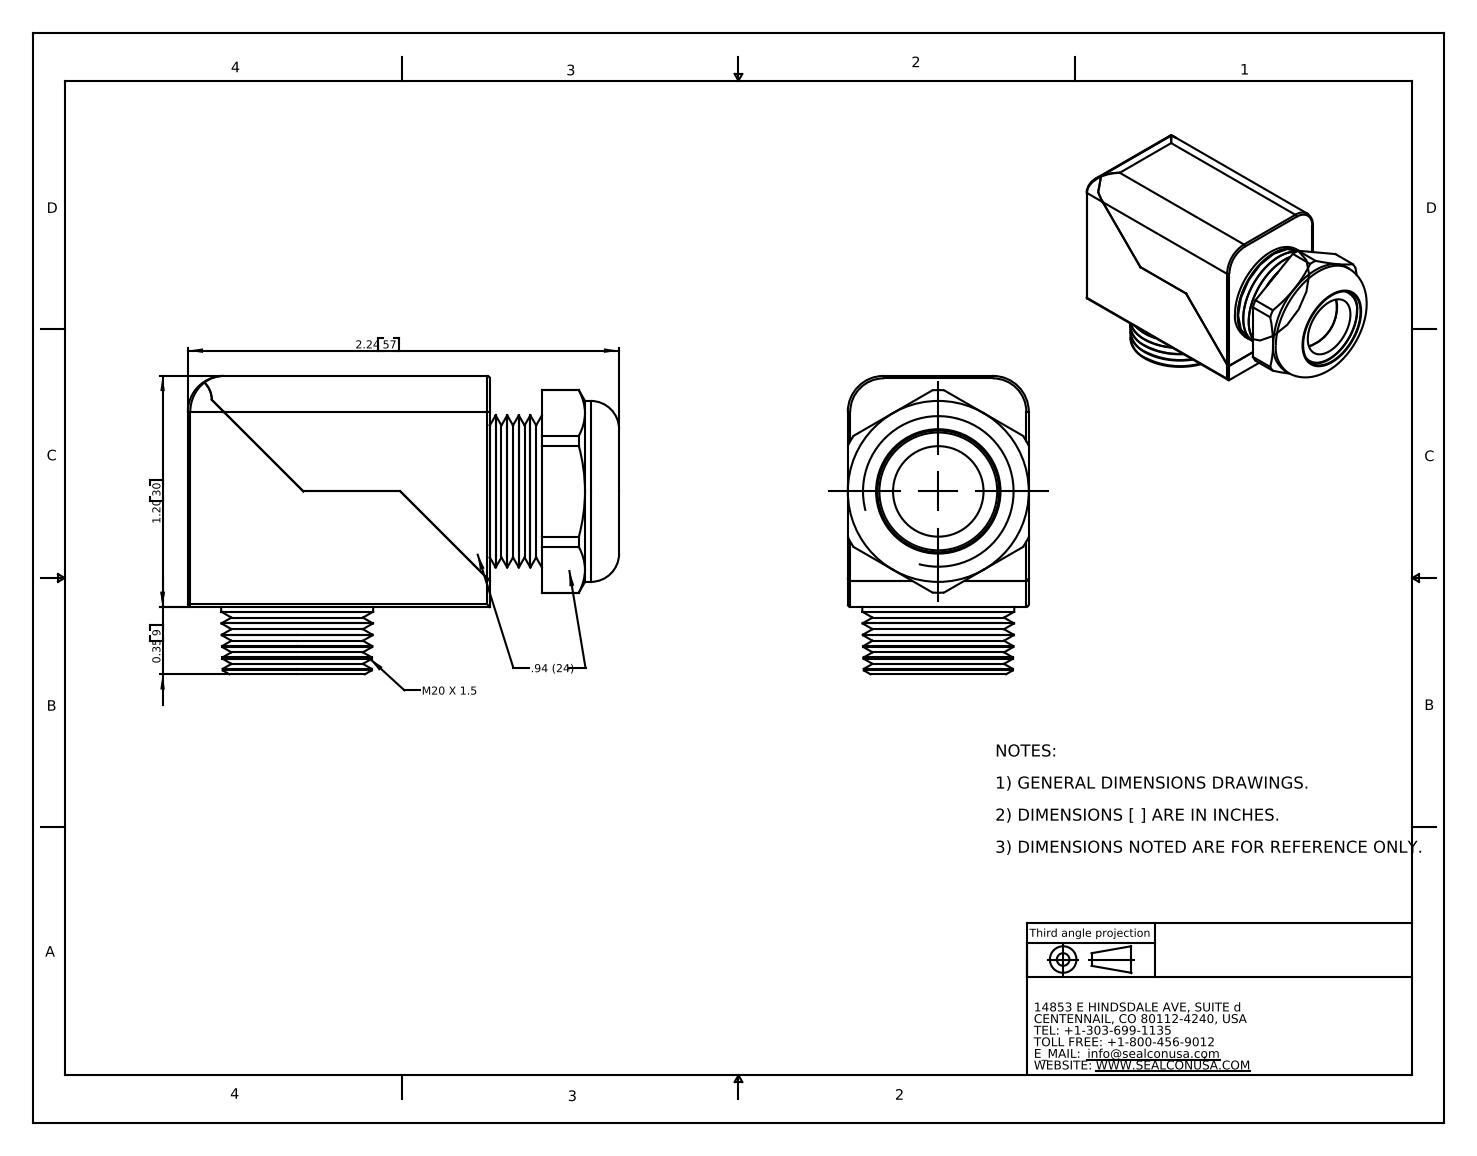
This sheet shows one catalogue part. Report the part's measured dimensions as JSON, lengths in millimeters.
{"part_name": "ED20MA-GY", "step_written_by": "SolidWorks 2007 (CONFIG_CONTROL_DESIGN)", "units": "millimeters", "bodies": {"solids": 3, "faces": 151, "planar": 29, "cylindrical": 48, "other": 74}, "overall_size": [56.9, 39.4, 23.9], "volume_mm3": 29820, "surface_area_mm2": 12930, "round_holes": [[11.9, 2], [16.1, 1]], "round_bosses_or_shafts": [[23.9, 1], [20.1, 1]], "partial_cylinders_radius": [[0.3, 8], [4.7, 3], [3.1, 1], [13.4, 1]], "face_to_face_distances": [23.9, 9, 15.2, 30.5, 39.8, 12.6, 52.4, 5.7, 6.9, 46.7]}
